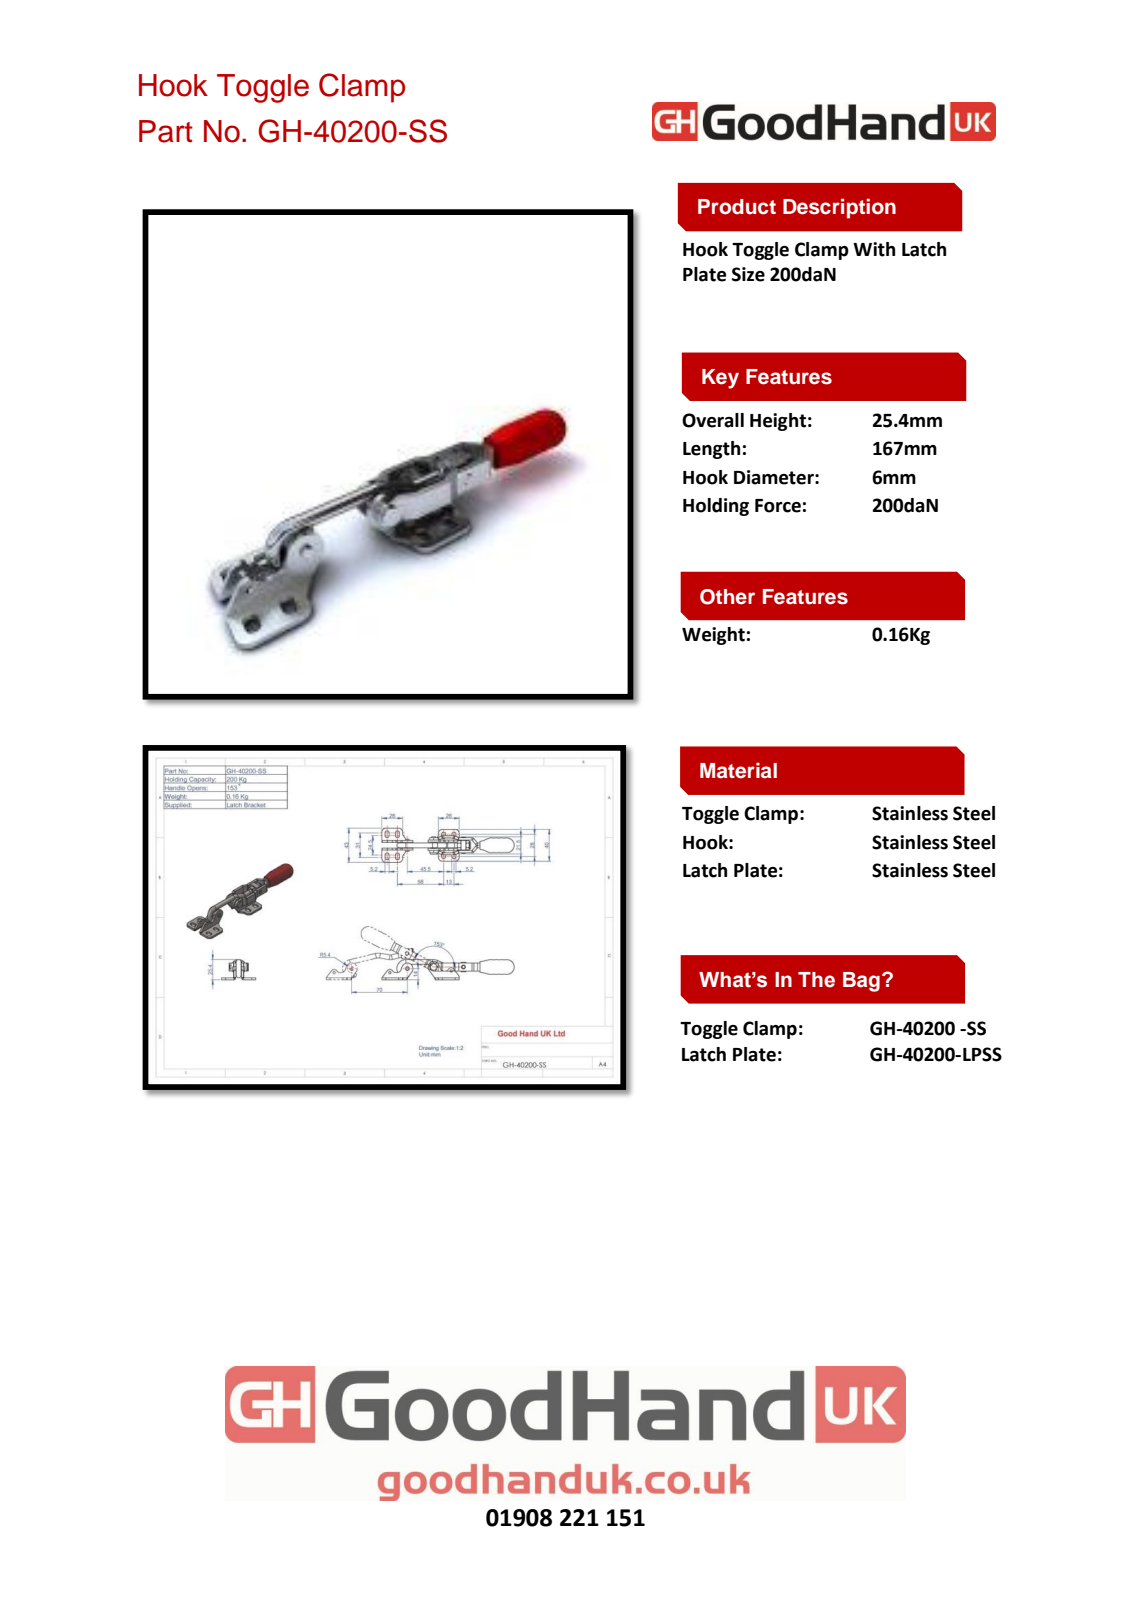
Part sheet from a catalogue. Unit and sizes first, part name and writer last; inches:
Units: inches
Overall size (bounding box): 6.575 × 1.693 × 0.994
Round holes (diameter × count): ⌀0.157 ×3, ⌀0.118 ×2, ⌀0.197 ×1, ⌀0.236 ×1, ⌀0.315 ×1
Round bosses / shafts (diameter × count): ⌀0.236 ×3, ⌀0.551 ×2, ⌀0.197 ×2, ⌀0.276 ×1
Partial cylindrical surfaces — rounded edges, fillets, slot ends (radius × count): R0.102 ×18, R0.119 ×12, R0.197 ×11, R0.098 ×4, R0.004 ×2, R0.02 ×2, R0.118 ×2, R0.157 ×2
Main face-to-face distances: 0.098, 0.118, 0.394, 0.02, 0.512, 0.492, 0.413, 0.63, 0.102, 0.22
Hole centre spacings: 0.888, 0.62, 1.341, 1.454, 2.207, 2.222, 2.794, 3.072
Volume: 1.532 in³ · Surface area: 27.82 in²
Bodies: 6 solids, 421 faces (184 planar, 153 cylindrical, 84 other)
Part name (STEP PRODUCT): Group2^GH-40200(簡化); Group5^GH-40200(簡化); GH-40200-SS(簡化); Group3^GH-40200(簡化) (+2 more)
STEP written by: SolidWorks 2016 (AUTOMOTIVE_DESIGN)
